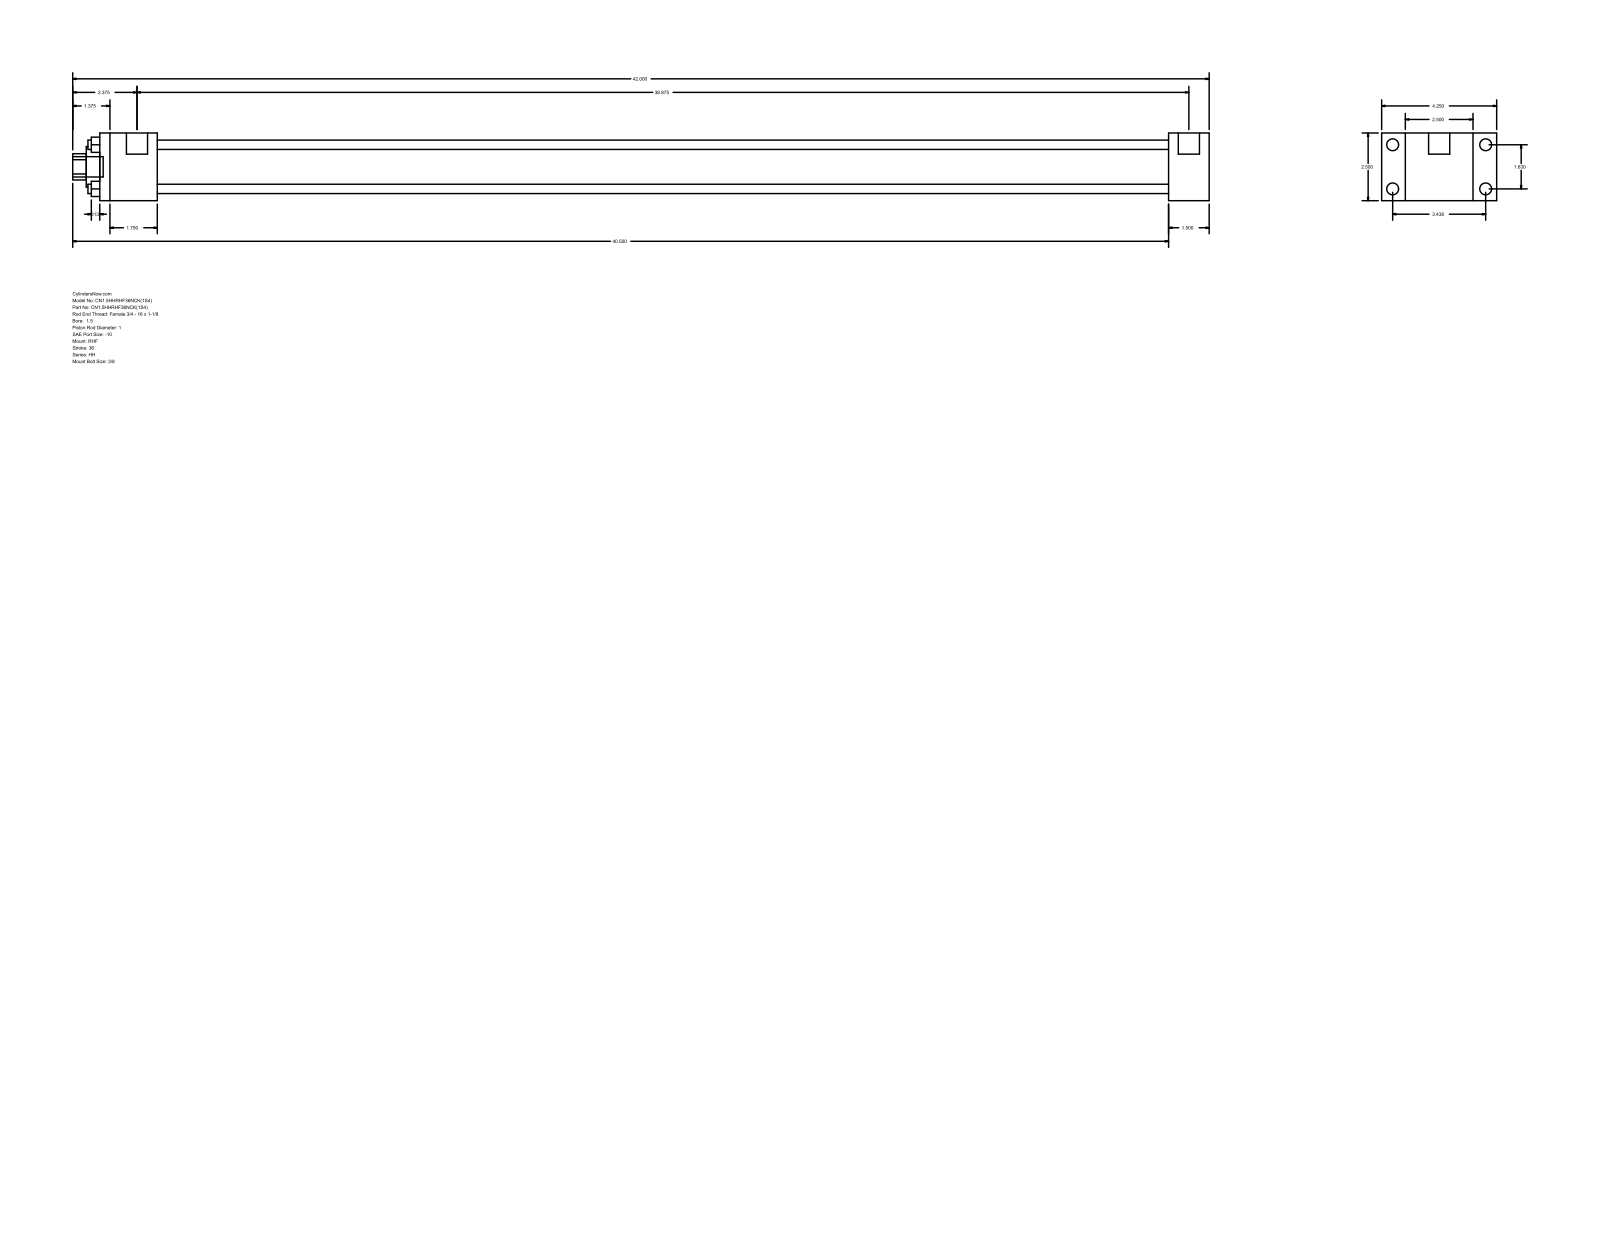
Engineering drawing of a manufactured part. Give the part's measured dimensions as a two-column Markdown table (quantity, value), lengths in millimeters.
| quantity | value |
| --- | --- |
| part name | HH_RHF__0150_1 |
| STEP written by | GSSL Pune (CONFIG_CONTROL_DESIGN) |
| units | millimeters |
| bodies | 0 solids, 88 faces (60 planar, 28 cylindrical, 0 other) |
| overall size | 1066.8 × 107.95 × 63.5 |
| round holes (diameter × count) | 8.76 × 4, 25.4 × 1, 38.1 × 1, 44.45 × 1 |
| round bosses / shafts (diameter × count) | 11.13 × 4, 5.56 × 4, 19.84 × 2, 19.05 × 1 |
| partial cylindrical surfaces (radius × count) | 12.29 × 1 |
| main face-to-face distances | 63.5, 22.23, 85.73, 38.1, 107.96, 949.32, 987.42, 53.98, 1003.3, 1041.4 |
| hole center spacings | 29.27, 41.4, 58.55 |
